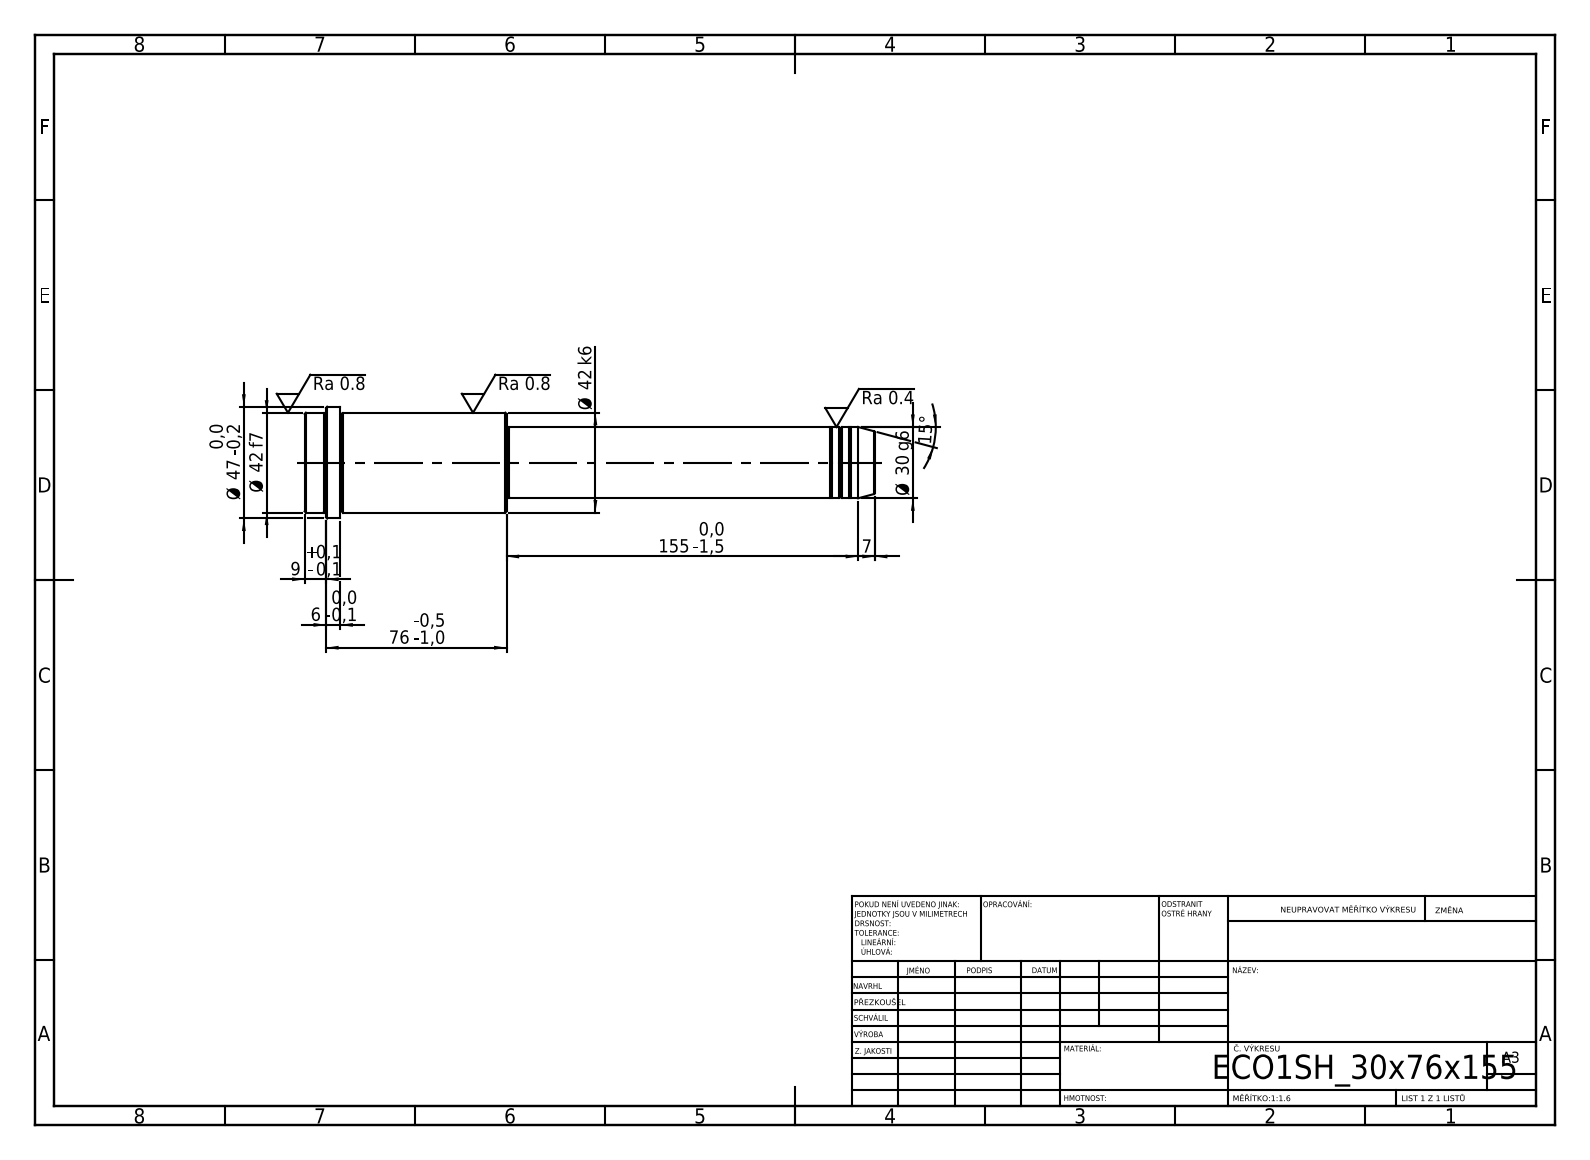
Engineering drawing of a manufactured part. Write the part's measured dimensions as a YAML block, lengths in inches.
step_written_by: "SolidWorks 2019 (CONFIG_CONTROL_DESIGN)"
units: inches
bodies: {solids: 1, faces: 52, planar: 6, cylindrical: 16, other: 30}
overall_size: [9.449, 1.85, 1.85]
volume: 13.95
surface_area: 45.66
round_bosses_or_shafts:
  - {diameter: 1.85, count: 1}
  - {diameter: 1.654, count: 1}
  - {diameter: 1.181, count: 1}
  - {diameter: 1.142, count: 1}
face_to_face_distances: [3.346, 6.102, 9.449, 8.858, 2.756, 0.591, 9.094, 2.992, 0.236, 0.354]
